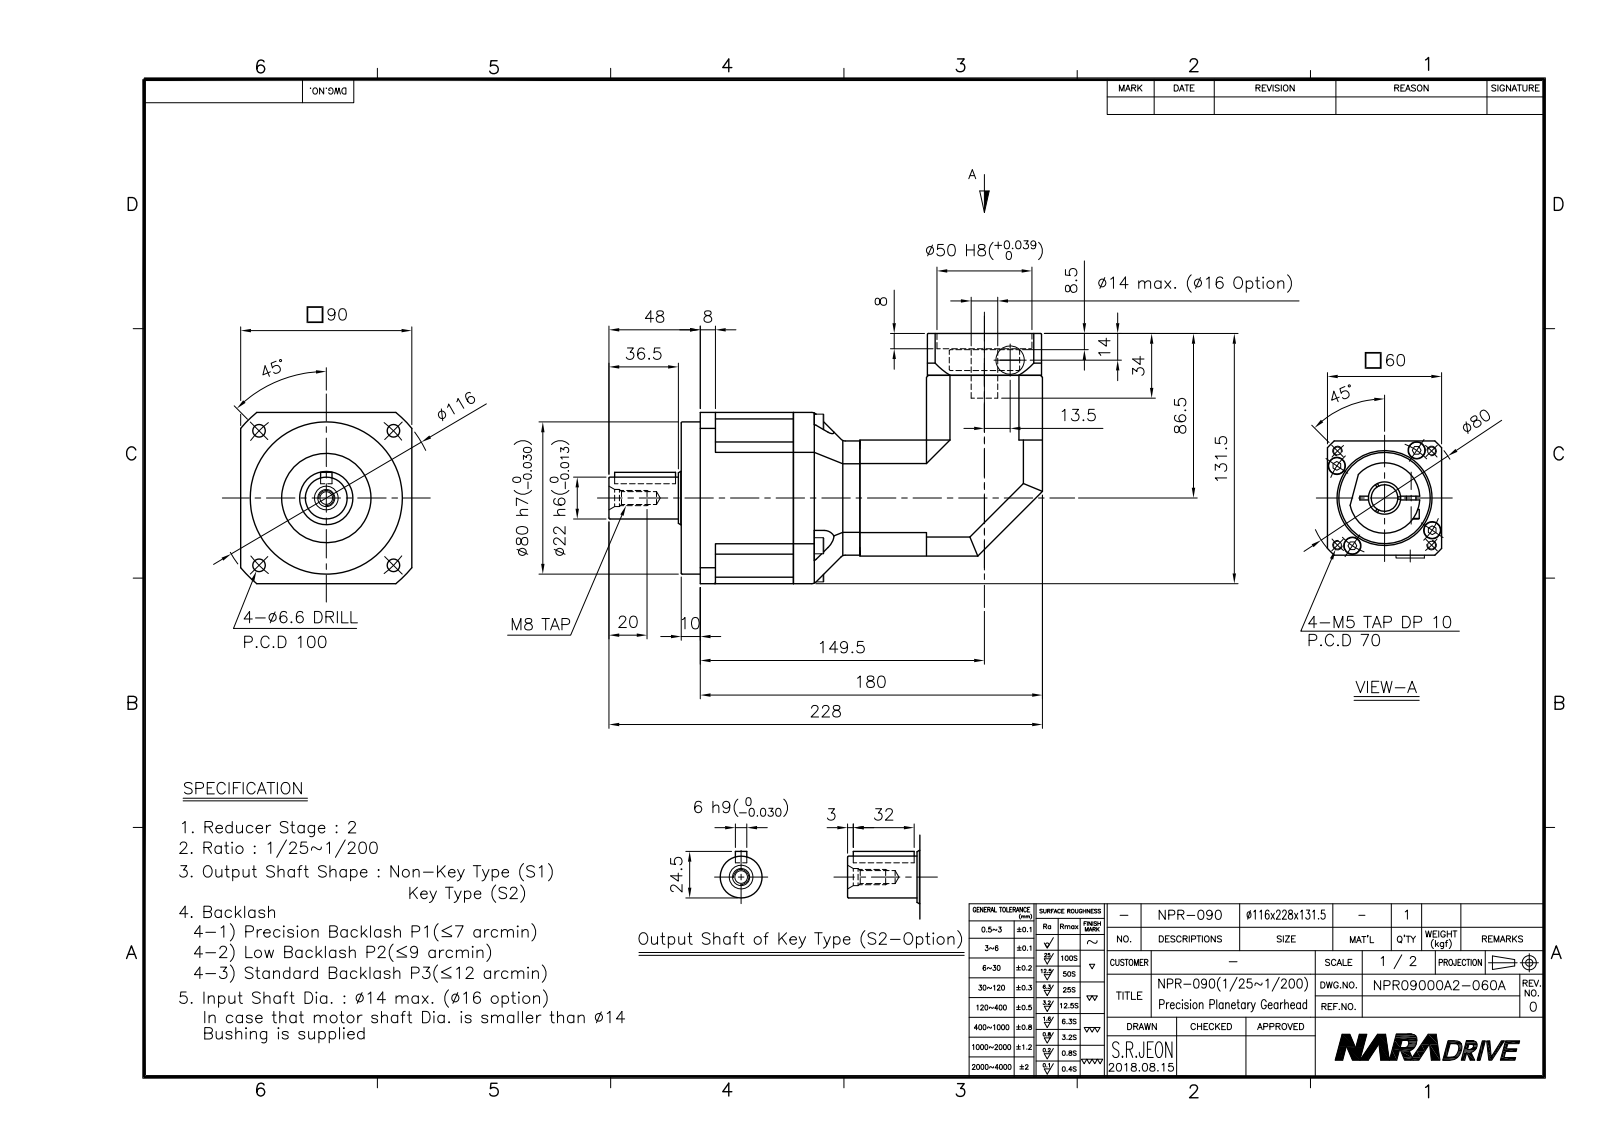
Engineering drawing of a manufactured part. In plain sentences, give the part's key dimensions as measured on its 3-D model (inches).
The part is named "NPR09000A2-060A-S1". Its 3-D file was written by "Autodesk Inventor 2015 (AUTOMOTIVE_DESIGN)". It is 2 solids with 522 faces: 253 planar, 140 cylindrical and 129 other. Overall it measures 8.976 by 5.177 by 3.543 inches. Its volume is 54.88 cubic inches and its surface area 198.3 square inches. Round holes: 12 of diameter 0.163, 9 of diameter 0.217, 5 of diameter 0.354, 4 of diameter 0.128, 4 of diameter 0.177, 4 of diameter 0.26, 4 of diameter 0.315, 1 of diameter 0.262, 1 of diameter 0.276, 1 of diameter 0.335, 1 of diameter 0.551, 1 of diameter 0.669. Round bosses or shafts: 9 of diameter 0.335, 9 of diameter 0.197, 4 of diameter 0.276, 4 of diameter 0.157, 1 of diameter 3.15, 1 of diameter 1.457, 1 of diameter 0.866, 1 of diameter 0.591. Partial cylindrical surfaces (rounded edges, fillets, slot ends): 8 of radius 0.118, 8 of radius 0.394, 4 of radius 0.02, 2 of radius 1.398, 1 of radius 0.081, 1 of radius 0.177, 1 of radius 1.378, 1 of radius 1.575. The main face-to-face distances are 0.571, 3.543, 2.972, 2.402, 1.614, 2.382, 0.315, 0.02, 2.008, 1.929. The hole center spacings are 1.191, 1.684, 2.52, 0.619, 2.557, 2.557, 2.784, 3.14.
